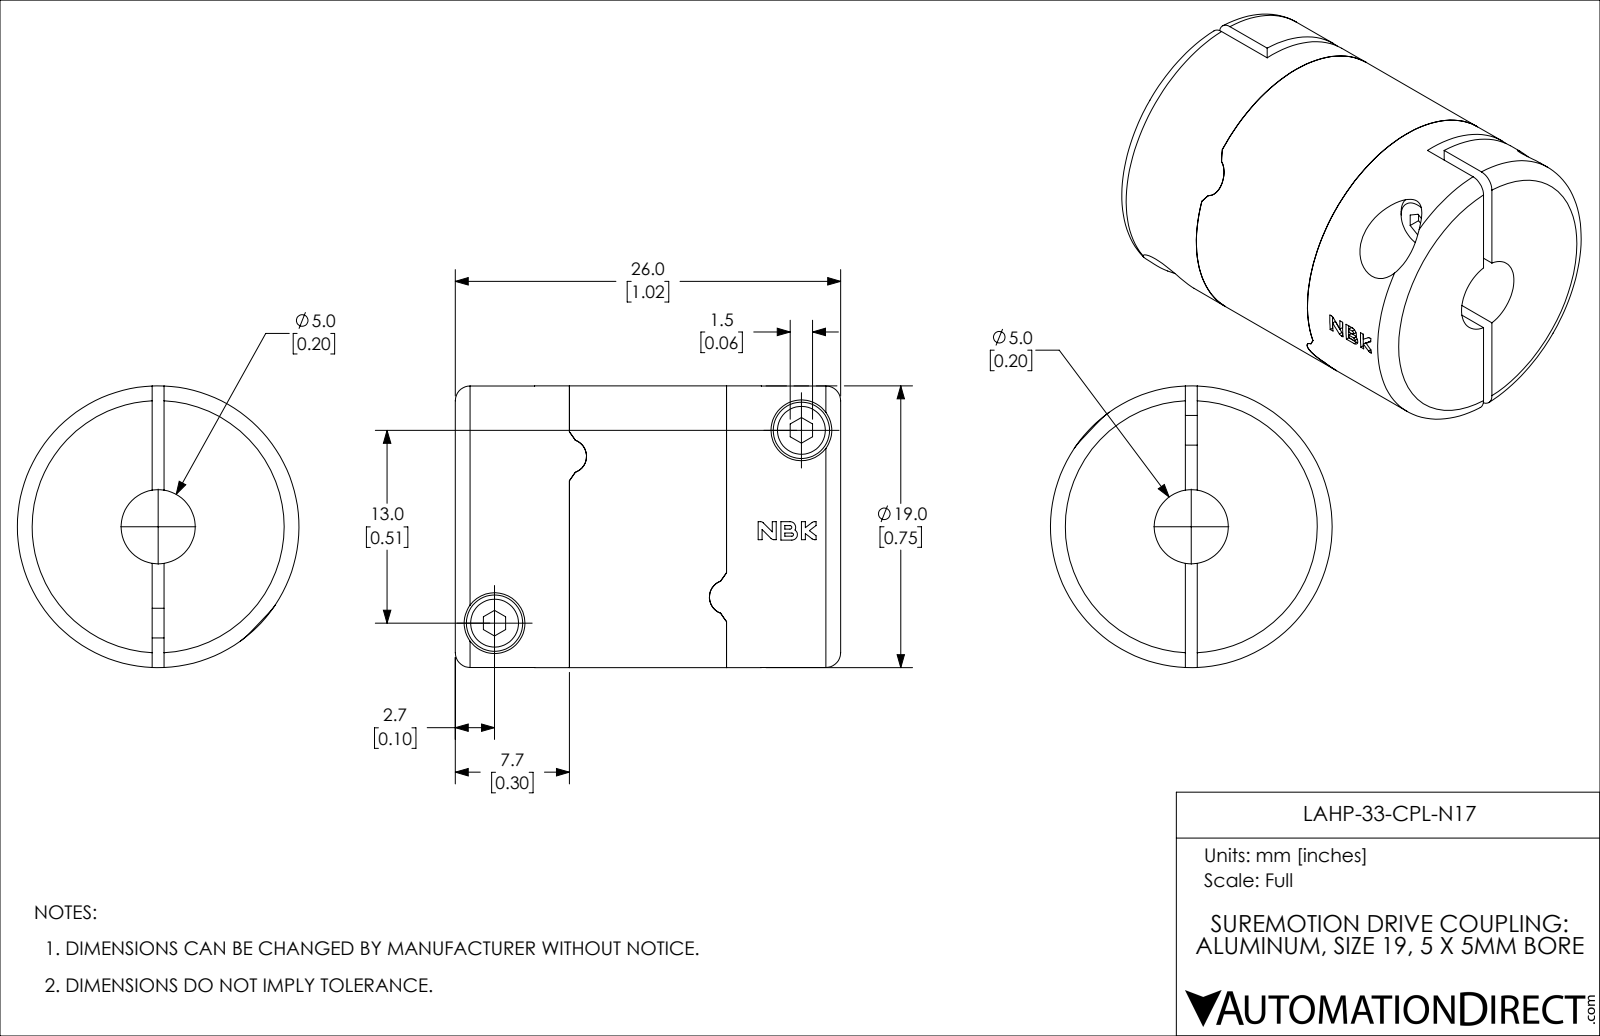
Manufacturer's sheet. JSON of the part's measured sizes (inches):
{"part_name": "LAHP-33-CPL-N17", "step_written_by": "SolidWorks 2019 (CONFIG_CONTROL_DESIGN)", "units": "inches", "bodies": {"solids": 3, "faces": 159, "planar": 89, "cylindrical": 56, "other": 14}, "overall_size": [1.024, 0.748, 0.748], "volume_in3": 0.389, "surface_area_in2": 6.966, "round_holes": [[0.079, 2], [0.098, 2], [0.161, 2], [0.197, 1], [0.217, 1]], "round_bosses_or_shafts": [[0.15, 2], [0.748, 1]], "partial_cylinders_radius": [[0.01, 4], [0.045, 2], [0.004, 1], [0.005, 1], [0.015, 1], [0.015, 1]], "face_to_face_distances": [0.417, 0.303, 0.72, 0.031, 0.211, 0.813, 0.093, 0.51, 0.179, 0.844], "hole_center_spacings": [0.962]}
